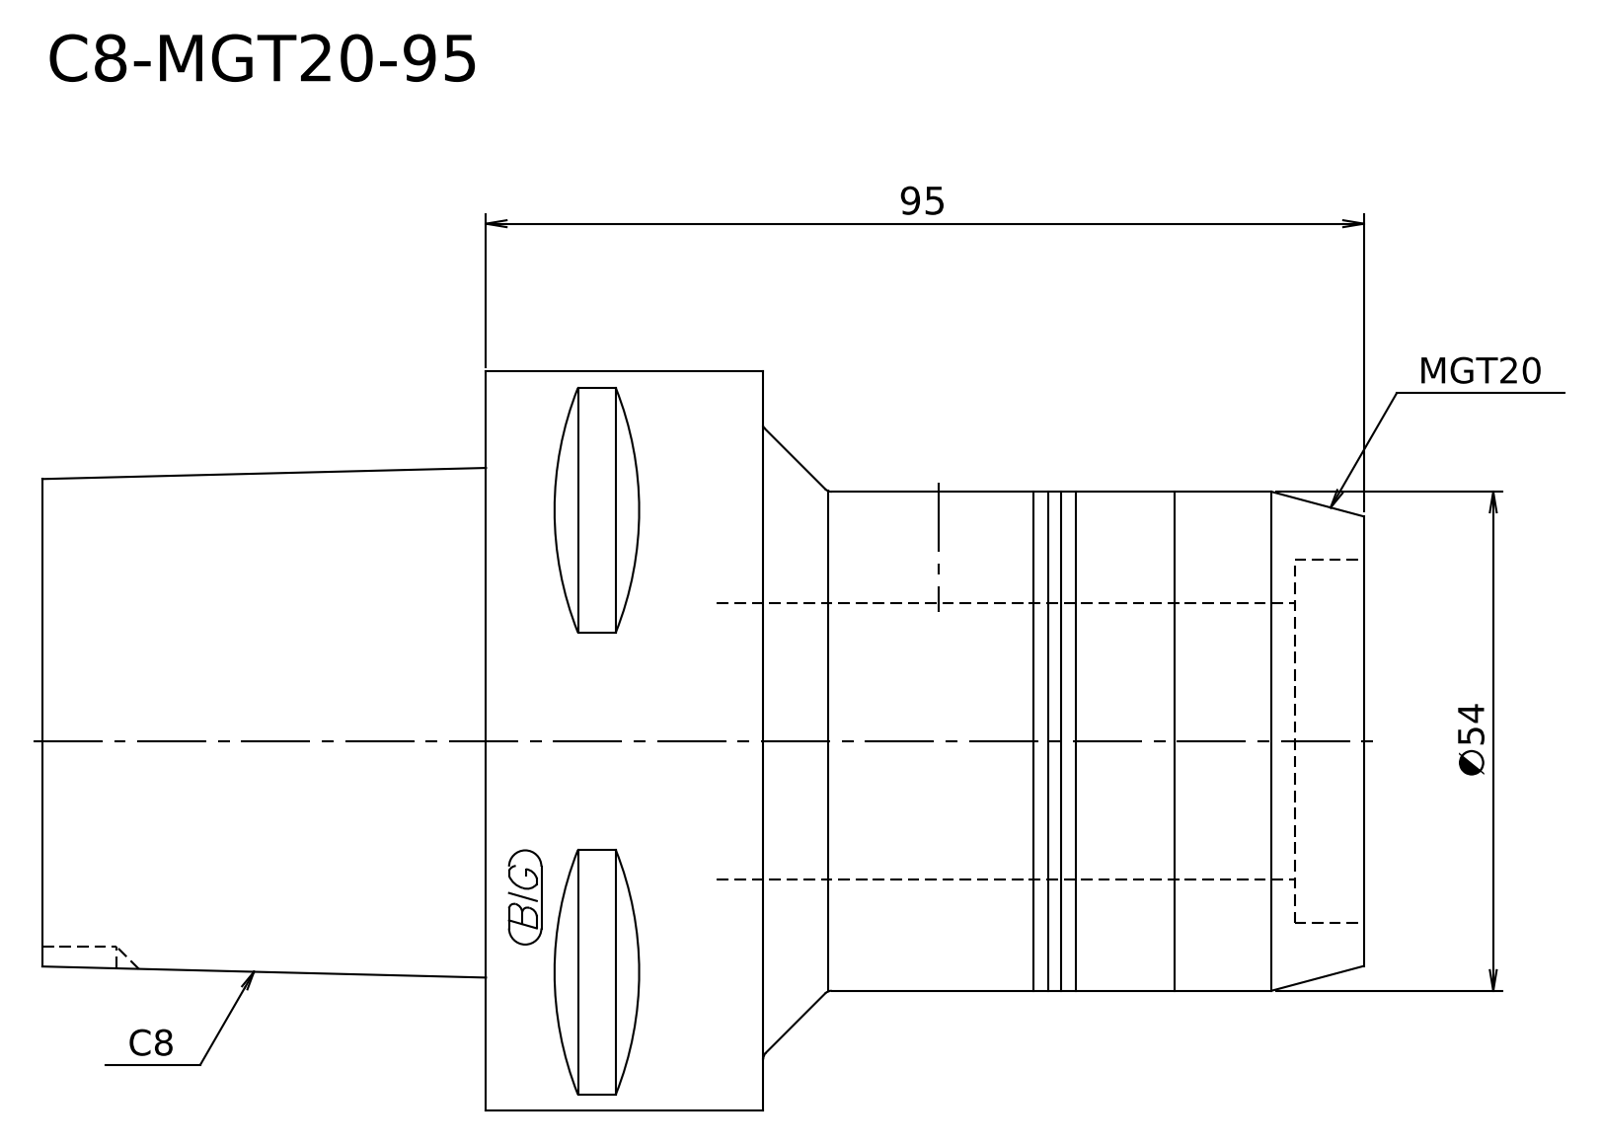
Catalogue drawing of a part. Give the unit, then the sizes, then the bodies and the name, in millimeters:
Units: millimetres
Overall size (bounding box): 143 × 79.98 × 79.98
Round bosses / shafts (diameter × count): ⌀79.98 ×1, ⌀54 ×1
Main face-to-face distances: 48, 95, 143, 65, 30, 78
Volume: 408 253 mm³ · Surface area: 35 458 mm²
Bodies: 1 solid, 9 faces (4 planar, 2 cylindrical, 3 other)
STEP written by: Kubotek KeyCreator V8.5.1 (14335) (CONFIG_CONTROL_DESIGN)
